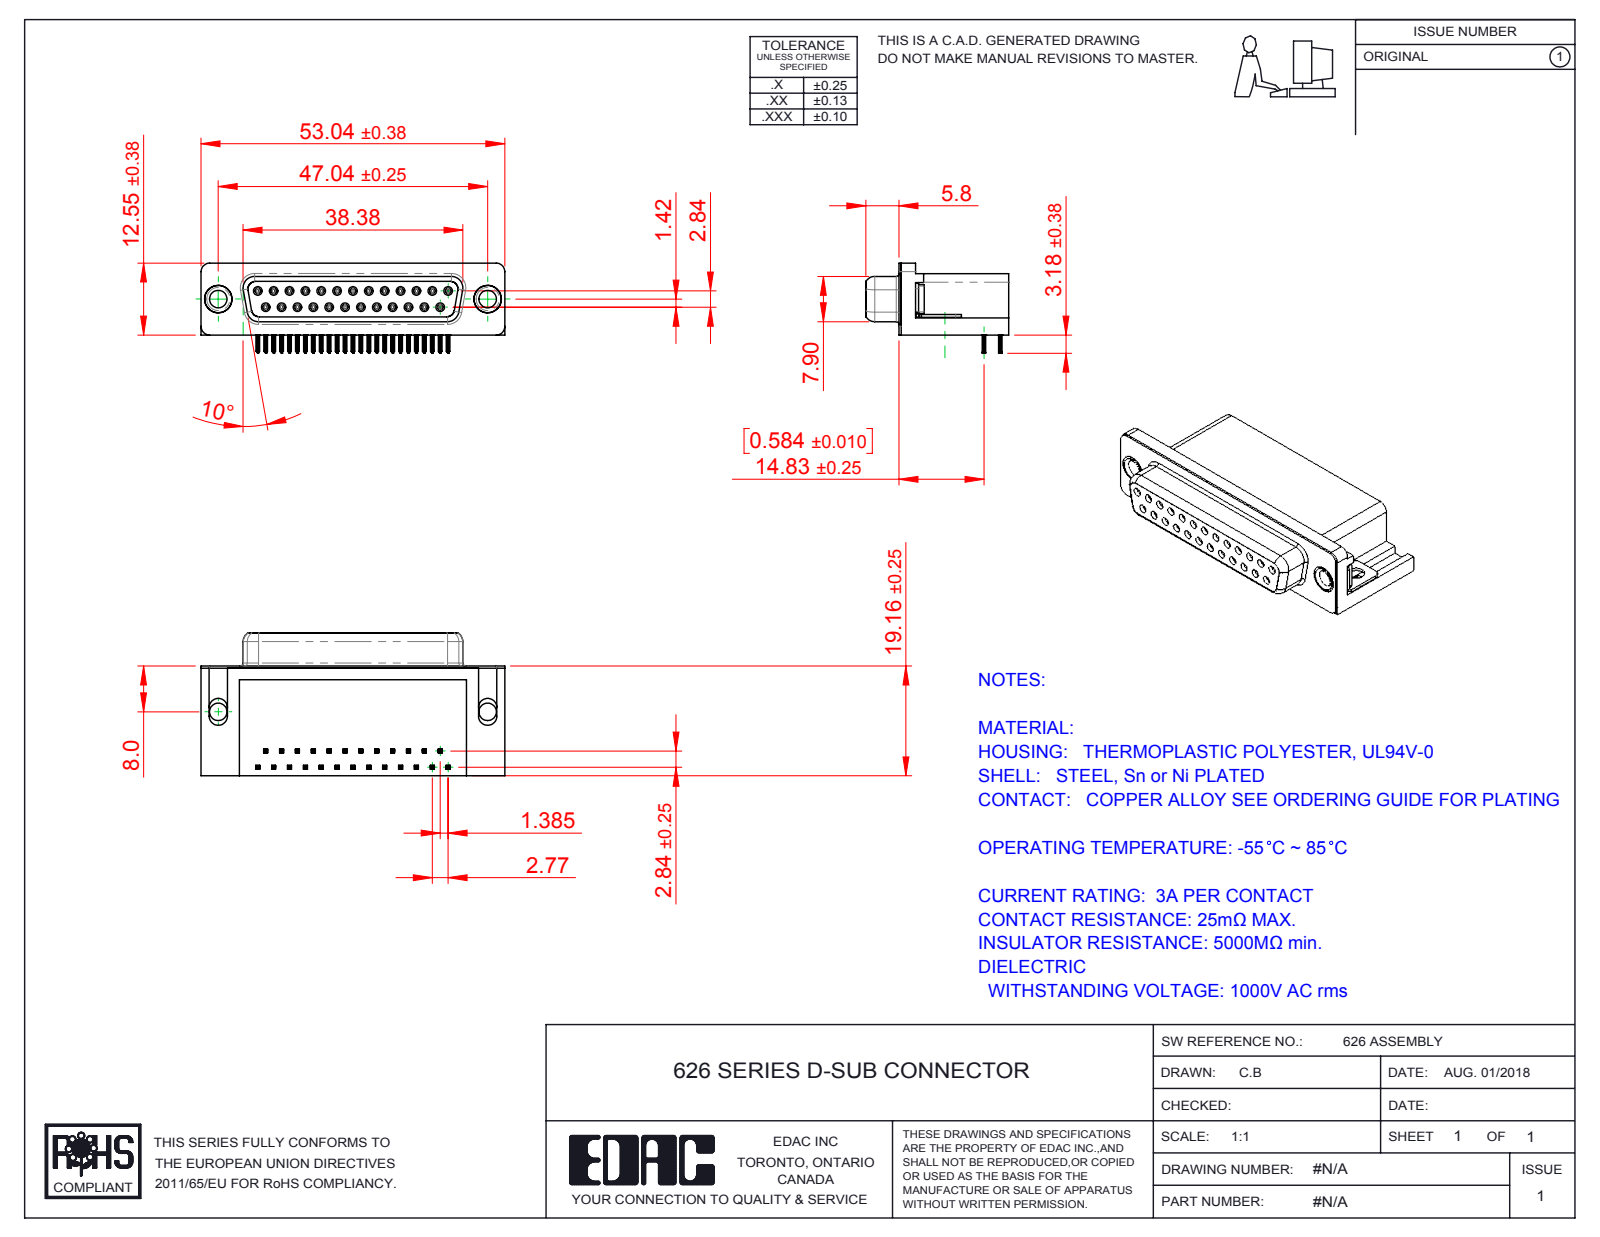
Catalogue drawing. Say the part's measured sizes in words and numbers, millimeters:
The part is named "626 Thru Hole Board Mount; 626 Contact Bottom; 626 Shell_25 Socket; 626 Thru Hole Rivet (+3 more)". Its 3-D file was written by "SolidWorks 2016 (CONFIG_CONTROL_DESIGN)". It is 31 solids with 3810 faces: 1722 planar, 902 cylindrical and 1186 other. Overall it measures 53.04 by 24.96 by 15.73 millimeters. Its volume is 10 656 cubic millimeters and its surface area 11 329 square millimeters. Round holes: 25 of diameter 0.8, 25 of diameter 0.9, 4 of diameter 3.05, 2 of diameter 4, 2 of diameter 4.8, 2 of diameter 5. Round bosses or shafts: 25 of diameter 1.2, 2 of diameter 4.9, 2 of diameter 4.75, 2 of diameter 3.85. Partial cylindrical surfaces (rounded edges, fillets, slot ends): 200 of radius 0.1, 100 of radius 0.15, 50 of radius 0.35, 25 of radius 0.34, 18 of radius 1, 12 of radius 0.28, 8 of radius 0.25, 8 of radius 1.35. The main face-to-face distances are 0.4, 10.35, 2.73, 18.76, 6.2, 0.85, 9.38, 3.18, 2.84, 0.35. The hole center spacings are 3.16, 2.77, 5.54, 8.31, 11.08, 5.03, 5.04, 7.48.
